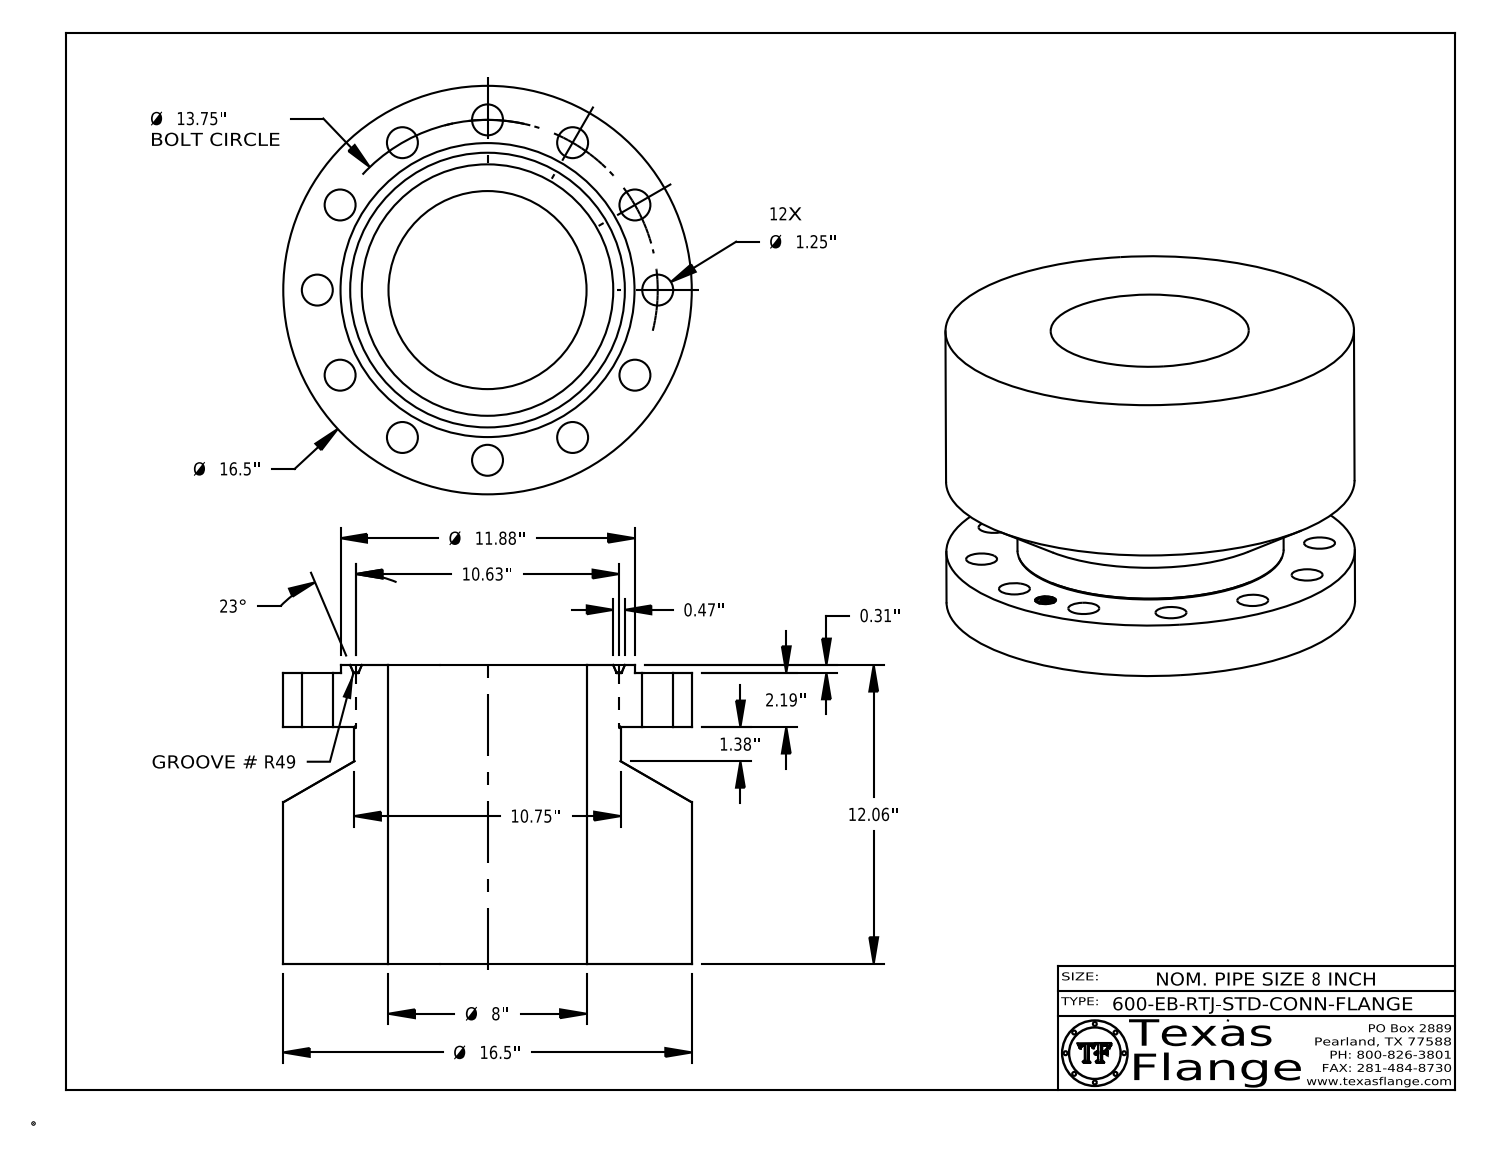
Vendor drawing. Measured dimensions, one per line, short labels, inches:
name: 8-600-EB-RTJ-STD-CONN-FLANGE
written by: CATIA V5 STEP AP214 (AUTOMOTIVE_DESIGN)
unit: in
bodies: 1 solid, 439 faces (371 planar, 54 cylindrical, 14 other)
size: 16.5 × 16.5 × 12.063
volume: 1 626 in³; area: 1 494 in²
holes: 12× ⌀1.25, 1× ⌀0.85, 1× ⌀8
bosses: 8× ⌀0.051, 1× ⌀16.5, 1× ⌀11.875, 1× ⌀10.75, 1× ⌀0.67
face distances: 9.56, 2.19, 11.75, 0.313, 2.503, 12.063, 2.498, 2.185, 9.565, 0.254
hole spacings: 6.875, 6.875, 9.723, 11.908, 13.281, 3.559, 3.559, 13.75
